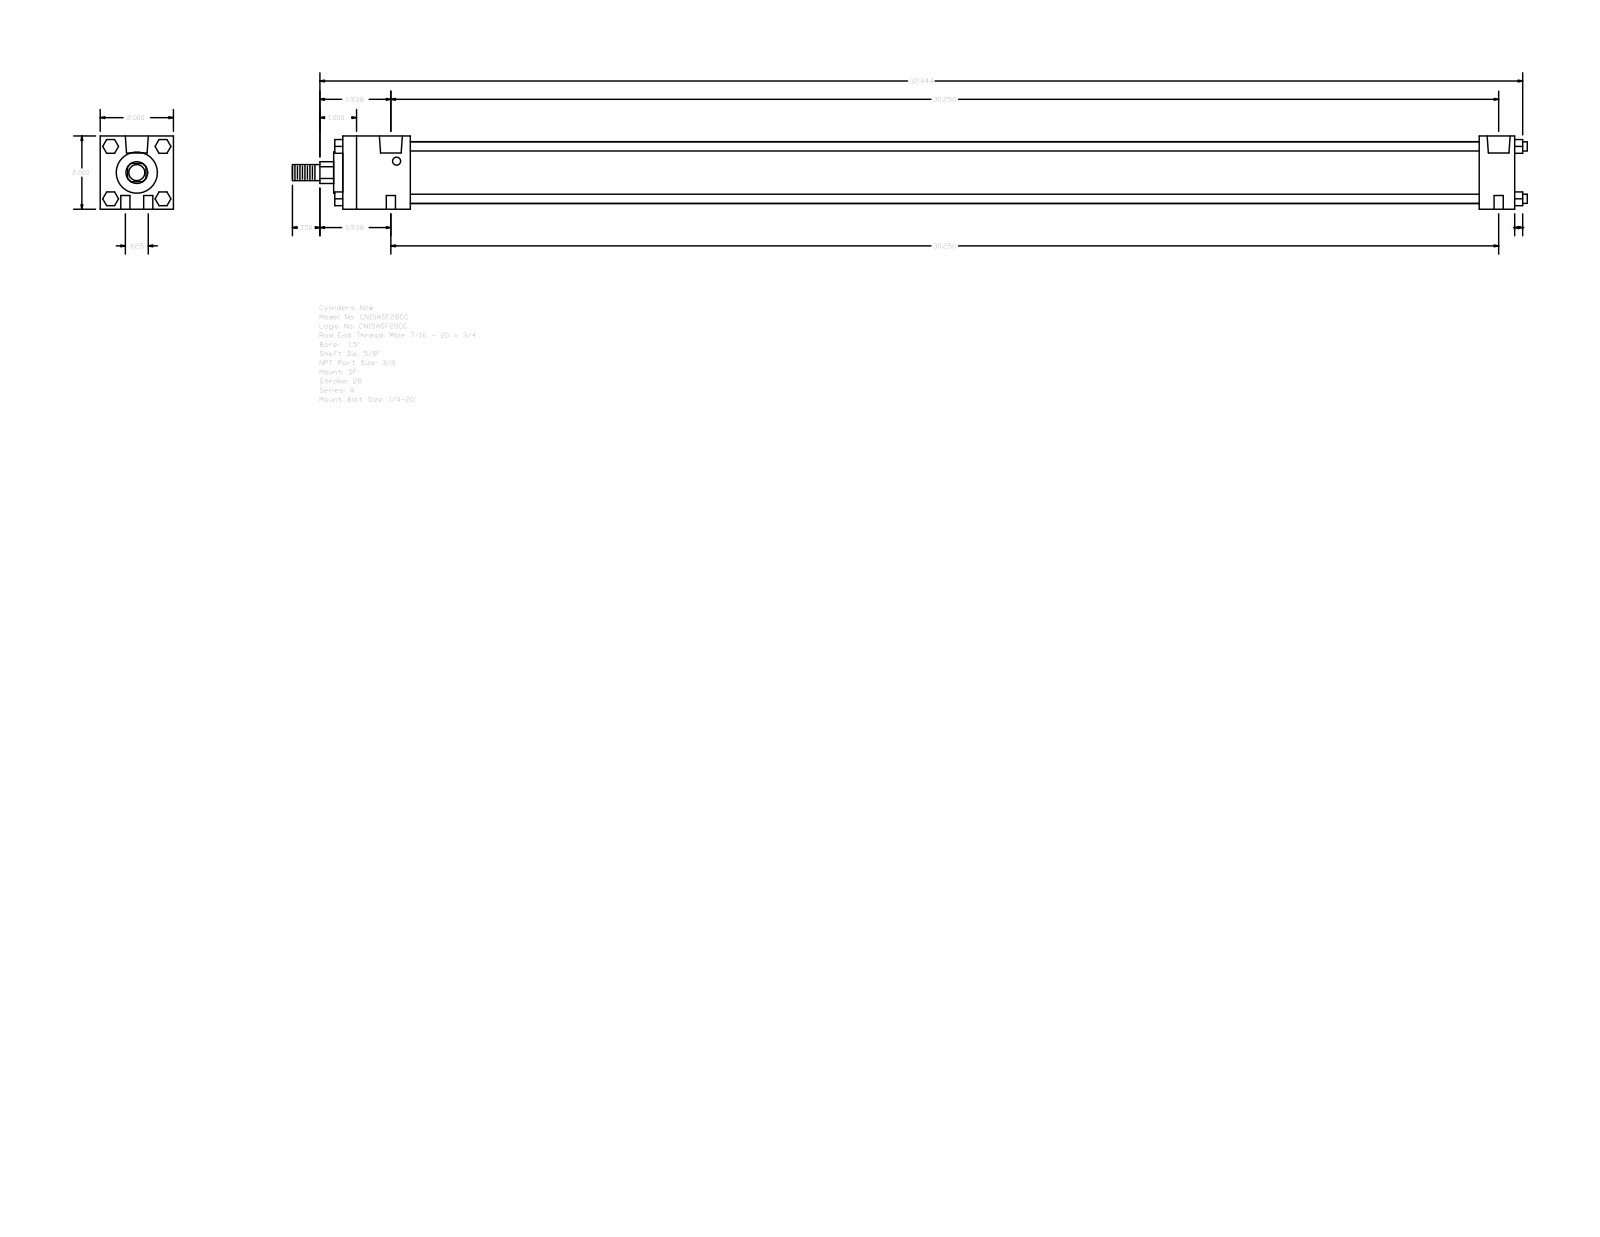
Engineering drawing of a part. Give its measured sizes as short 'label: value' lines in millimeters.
name: A_SF__0150_0.625
written by: GSSL Pune (CONFIG_CONTROL_DESIGN)
unit: mm
bodies: 0 solids, 124 faces (94 planar, 30 cylindrical, 0 other)
size: 856.46 × 50.8 × 50.8
holes: 4× ⌀6.35, 2× ⌀5.56, 2× ⌀15.93
bosses: 4× ⌀6.35, 1× ⌀42.93, 1× ⌀28.57, 1× ⌀15.88, 1× ⌀11.11
rounds: 1× R7.54
face distances: 50.8, 812.79, 46.83, 788.19, 741.36, 765.96, 24.6, 6.35, 9.52, 53.18
hole spacings: 7.94, 768.39, 768.35, 15.88, 768.51, 760.41
